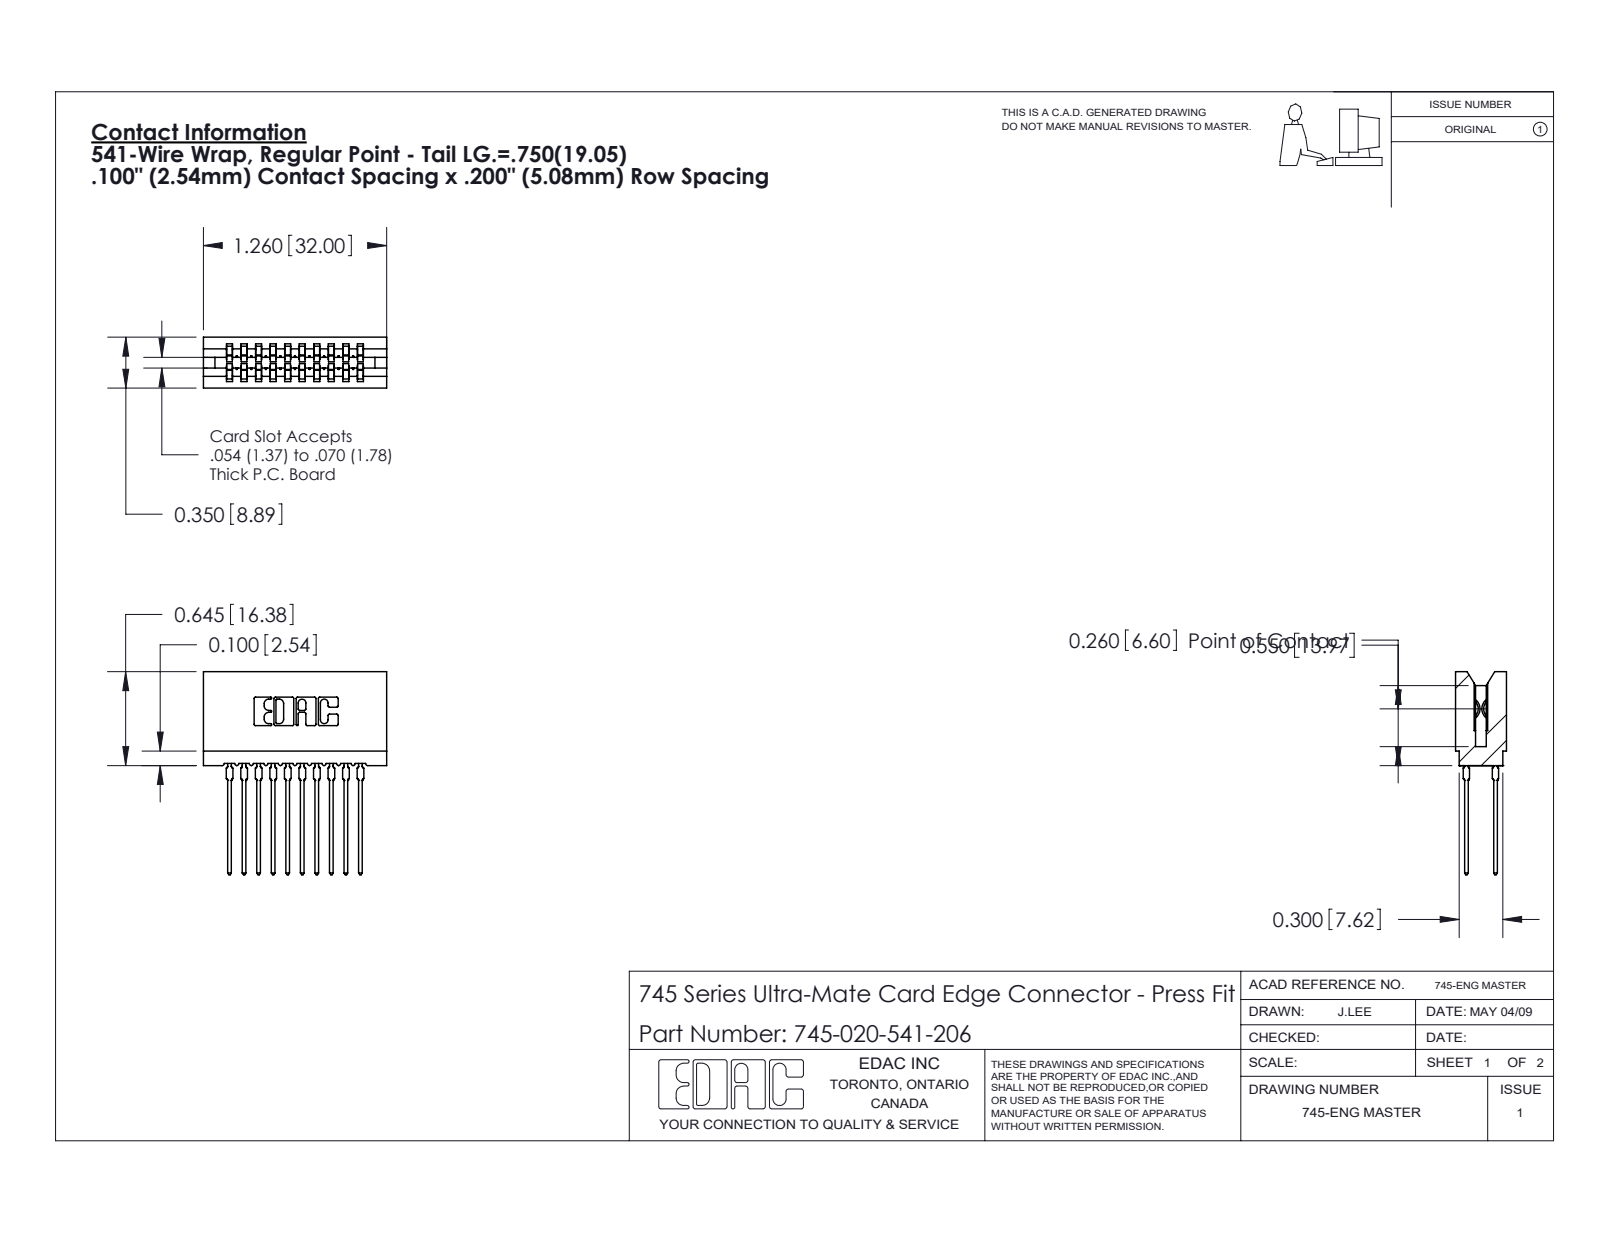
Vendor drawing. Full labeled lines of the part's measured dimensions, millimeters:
Part name (STEP PRODUCT): 745-020-541-206; 745-292-001_541; 745 Part_Insulator Option - 06
STEP written by: SolidWorks 2020 (CONFIG_CONTROL_DESIGN)
Units: millimetres
Bodies: 21 solids, 1886 faces (976 planar, 390 cylindrical, 520 other)
Overall size (bounding box): 35.5 × 32 × 8.9
Volume: 3 150 mm³ · Surface area: 6 089 mm²
Partial cylindrical surfaces — rounded edges, fillets, slot ends (radius × count): R0.5 ×40, R0.3 ×22, R0.4 ×20, R0.1 ×8, R0.3 ×8, R0.2 ×6, R0.8 ×6, R0.7 ×3
Main face-to-face distances: 5.1, 2.5, 7.6, 10.2, 1.1, 3.6, 12.7, 1.5, 6.1, 4
